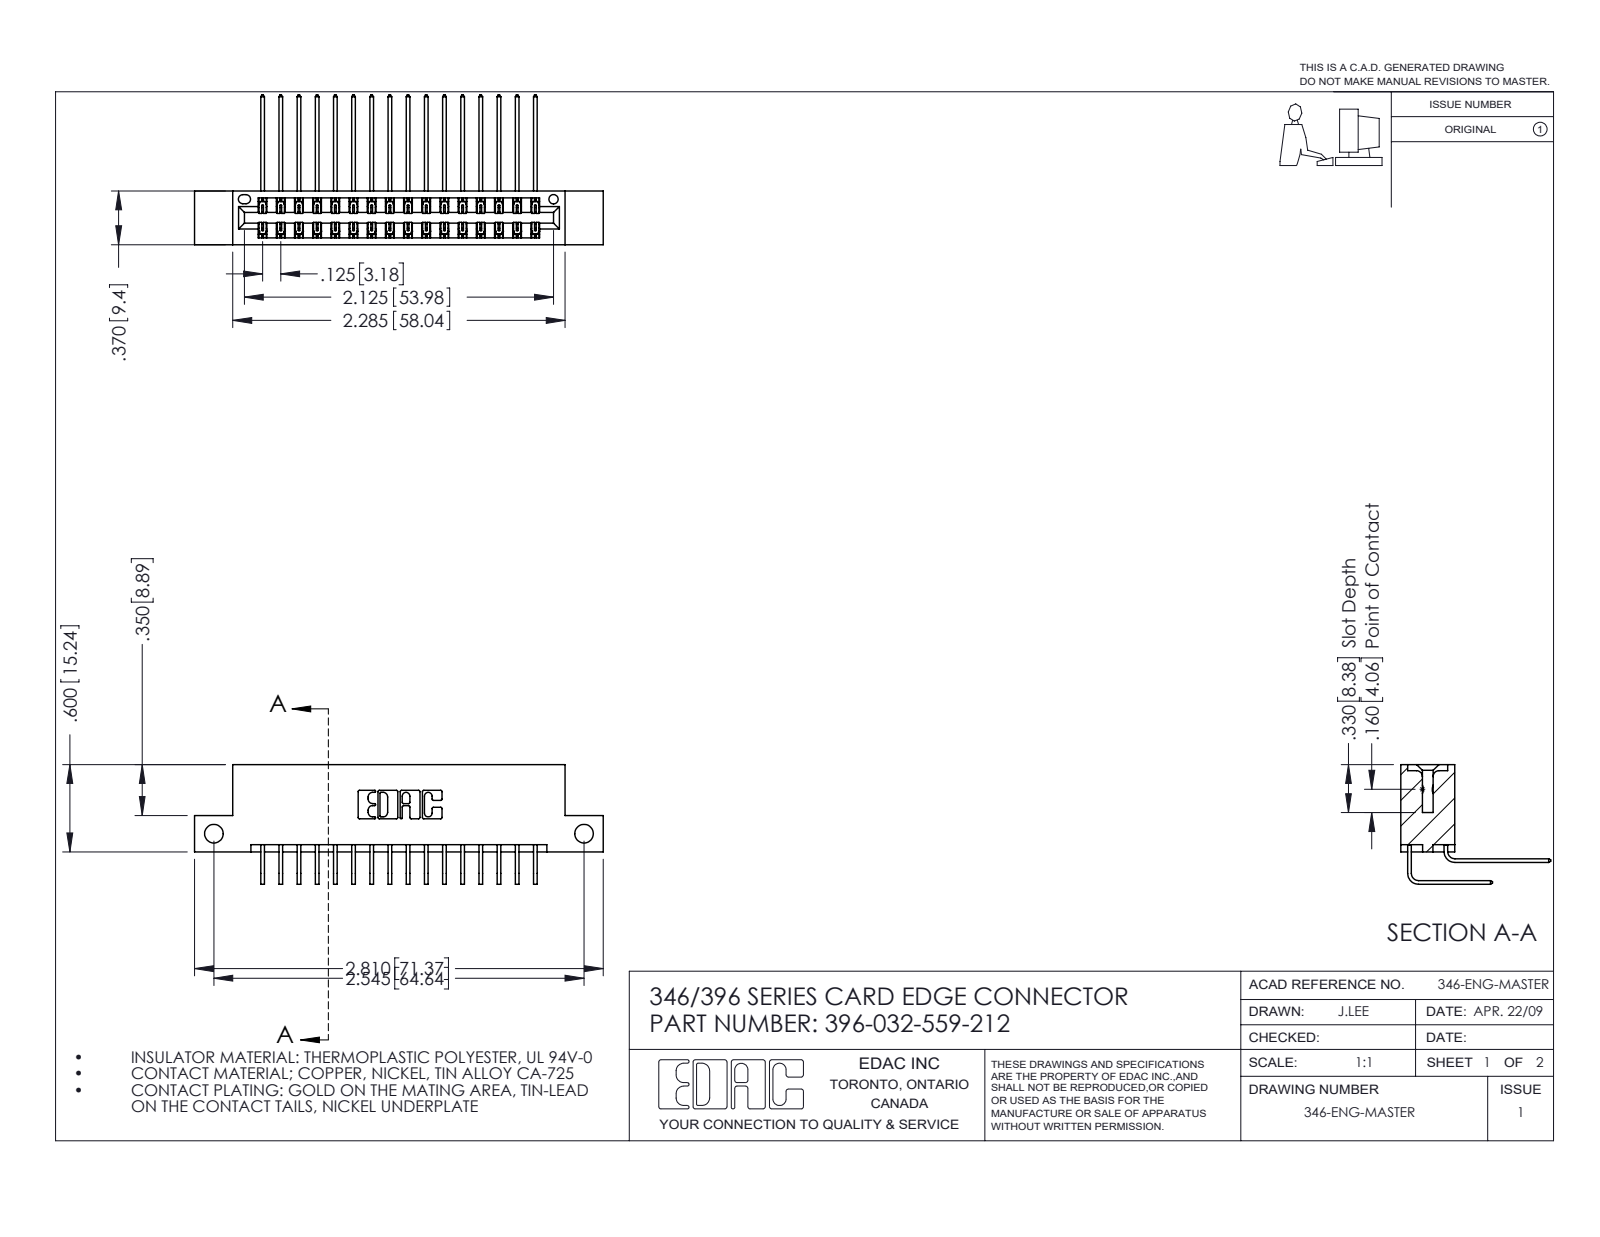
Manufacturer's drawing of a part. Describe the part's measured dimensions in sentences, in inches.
The part is named "345-292-001_558 559 Tail - 1; 346 Part_Flush Mounting Lugs - Side Mount; 345-292-001_559 Tail - 2; 396-032-559-212". Its 3-D file was written by "SolidWorks 2016 (CONFIG_CONTROL_DESIGN)". It is 33 solids with 1850 faces: 1260 planar, 590 cylindrical and 0 other. Overall it measures 2.81 by 1.03 by 0.823 inches. Its volume is 0.418 cubic inches and its surface area 15.13 square inches. Round holes: 2 of diameter 0.128, 1 of diameter 0.064. Partial cylindrical surfaces (rounded edges, fillets, slot ends): 48 of radius 0.006, 22 of radius 0.01, 6 of radius 0.007, 6 of radius 0.031, 3 of radius 0.026, 2 of radius 0.014, 2 of radius 0.022, 2 of radius 0.024. The main face-to-face distances are 0.048, 0.322, 0.25, 0.025, 0.37, 0.072, 0.298, 0.275, 0.148, 0.222. The hole center spacings are 2.545.
